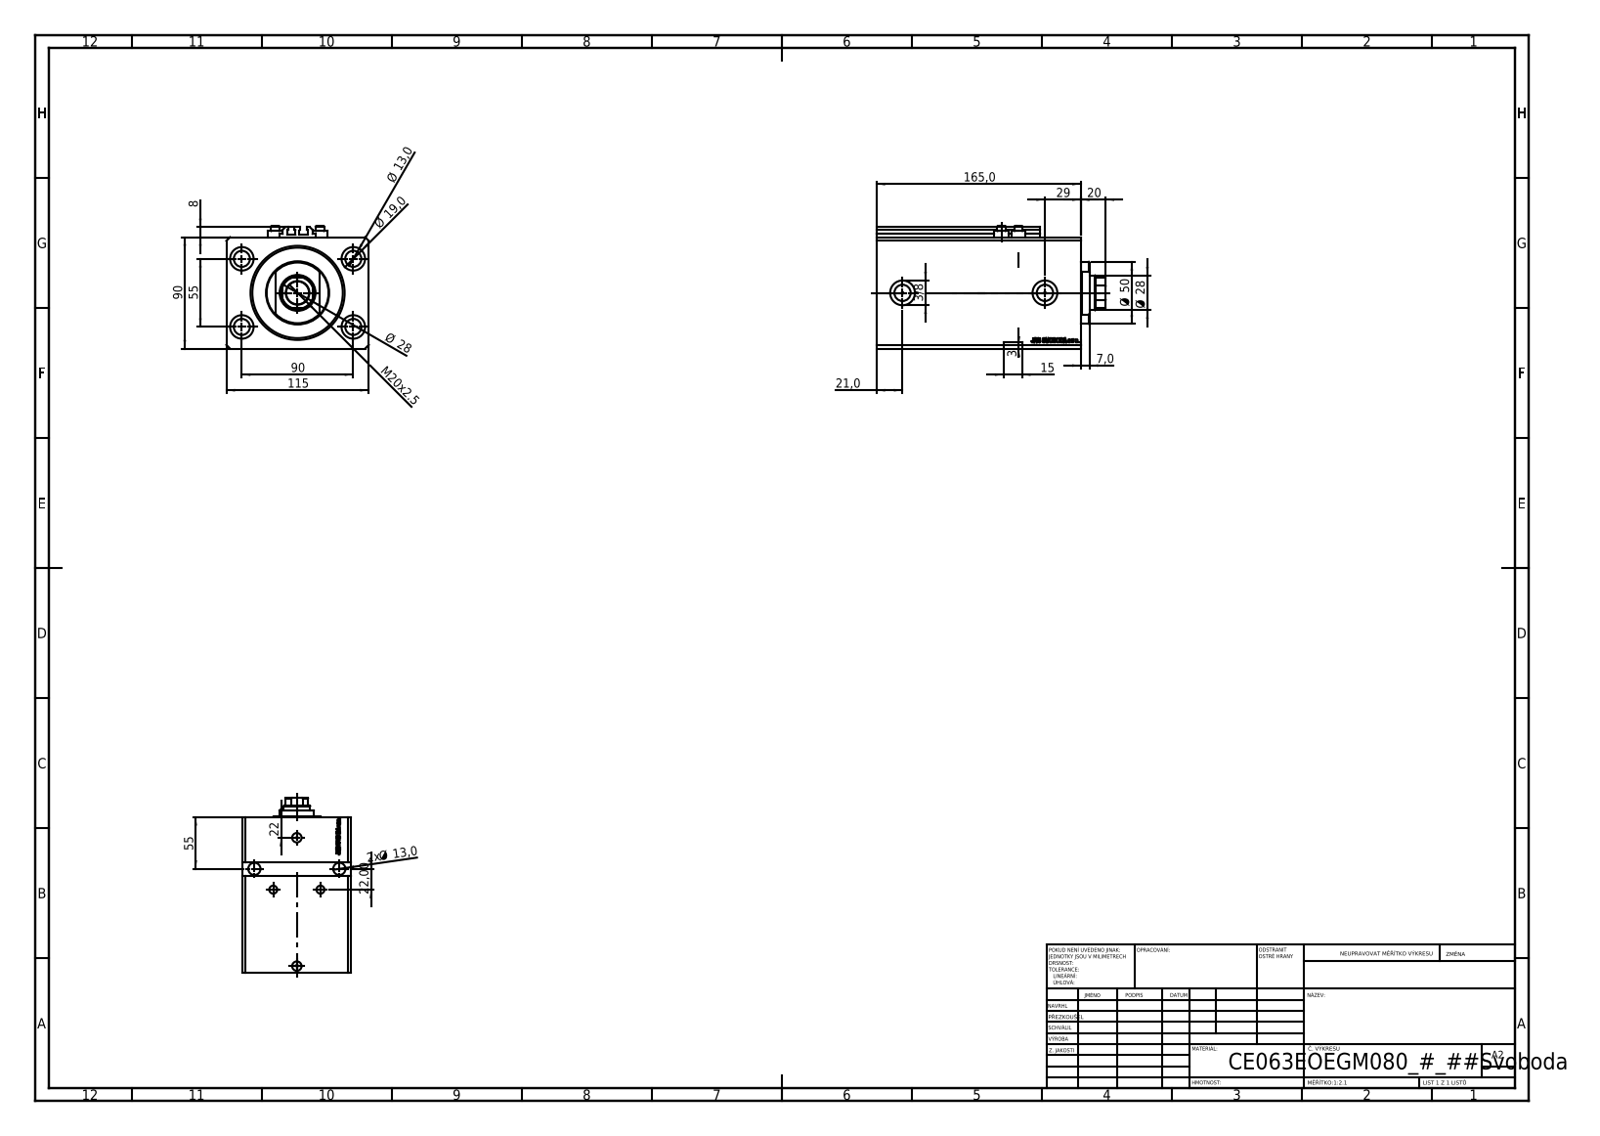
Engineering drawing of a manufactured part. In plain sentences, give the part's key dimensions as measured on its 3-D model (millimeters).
The part is named "V250CE_C_VCP; ALLEN BOLT V250CE; V250CE_E_Body; V250CE_VC_E". Its 3-D file was written by "SolidWorks 2019 (CONFIG_CONTROL_DESIGN)". It is 8 solids with 1115 faces: 543 planar, 134 cylindrical and 438 other. Overall it measures 185 by 115 by 99 millimeters. Its volume is 1 394 000 cubic millimeters and its surface area 213 348 square millimeters. Round holes: 6 of diameter 13, 4 of diameter 1.25, 4 of diameter 4, 4 of diameter 19, 2 of diameter 8.5, 2 of diameter 10, 2 of diameter 13.16, 2 of diameter 20, 1 of diameter 18.5, 1 of diameter 28, 1 of diameter 63, 1 of diameter 76. Round bosses or shafts: 4 of diameter 11.6, 4 of diameter 7, 1 of diameter 50. Partial cylindrical surfaces (rounded edges, fillets, slot ends): 10 of radius 0.2, 1 of radius 13.5. The main face-to-face distances are 90, 115, 165, 20, 17.9, 147.1, 145, 127.1, 65, 80. The hole center spacings are 52.74, 90, 13.6, 14.76, 27.39, 27.51, 28.46, 29.73.
